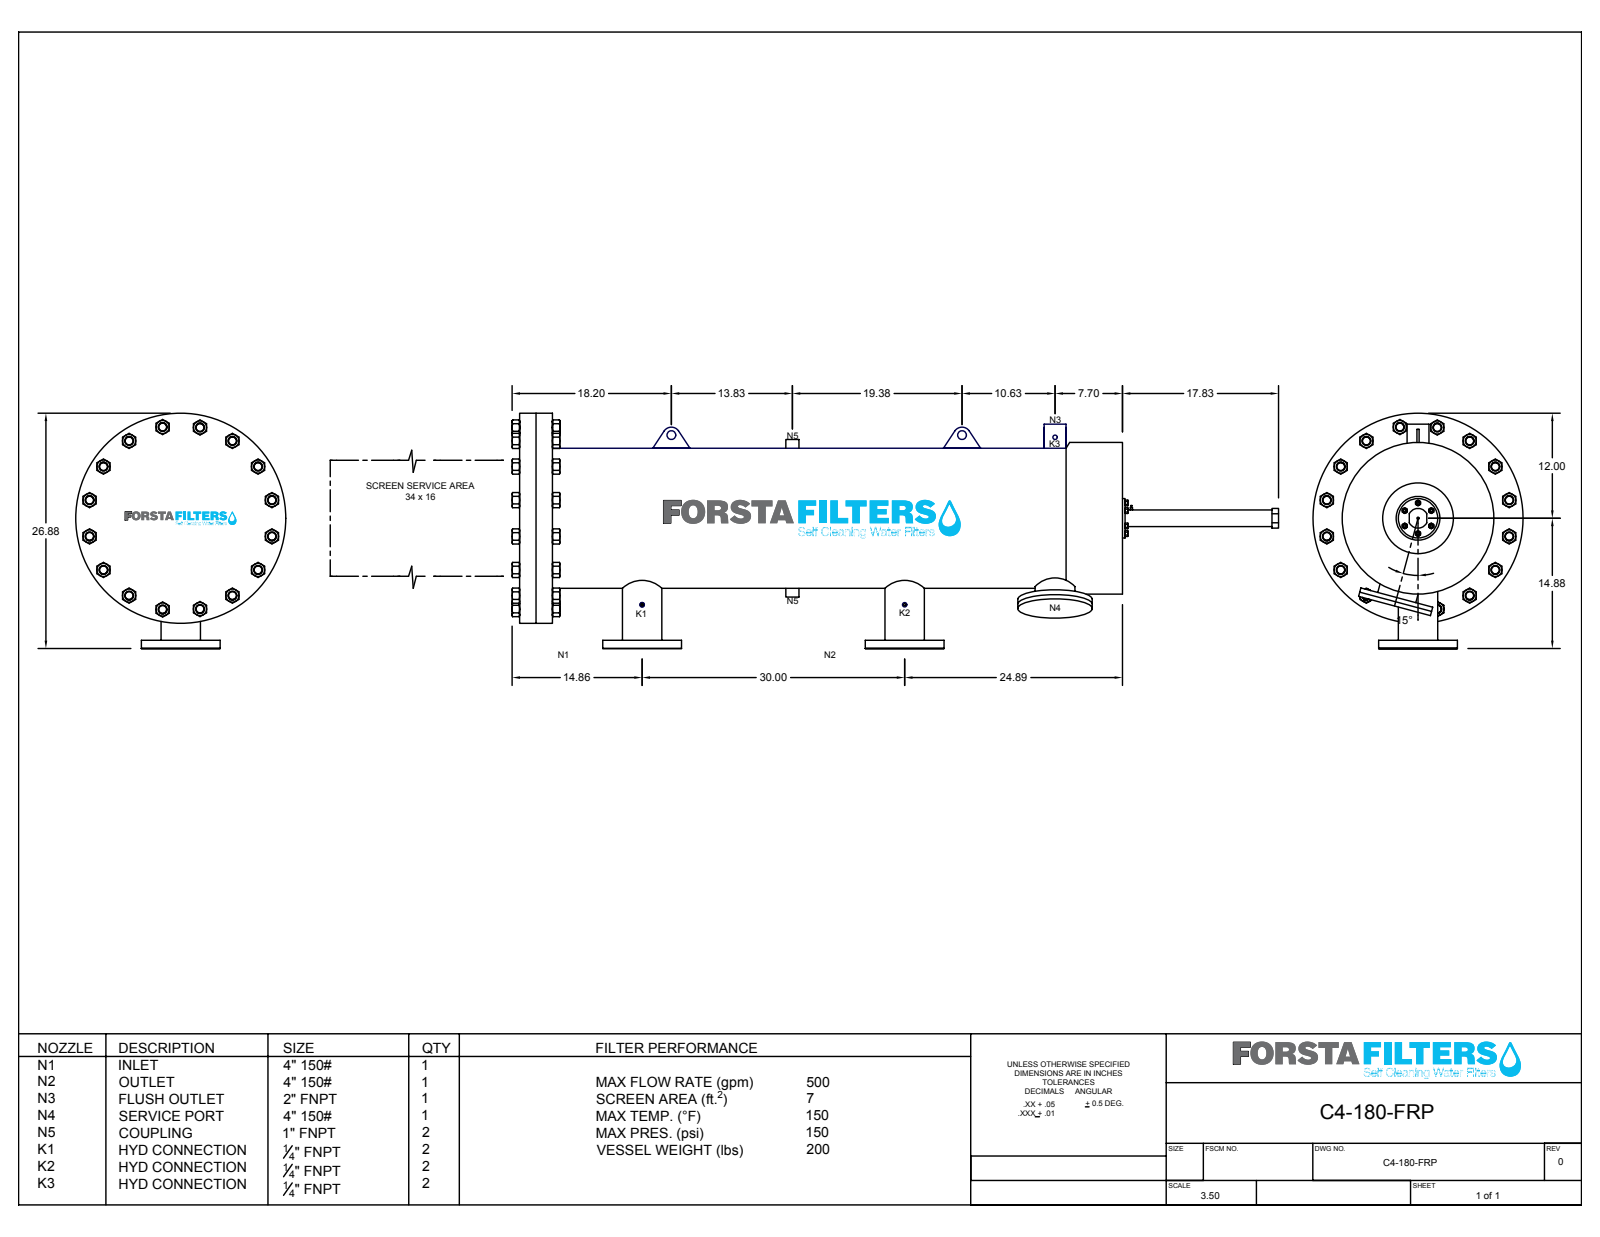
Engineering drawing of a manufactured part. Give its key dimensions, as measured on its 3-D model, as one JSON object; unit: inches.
{"part_name": "C4-FRP-180", "step_written_by": "SolidWorks 2018 (CONFIG_CONTROL_DESIGN)", "units": "inches", "bodies": {"solids": 22, "faces": 696, "planar": 362, "cylindrical": 330, "other": 4}, "overall_size": [87.395, 26.874, 24], "volume_in3": 2336, "surface_area_in2": 10796, "round_holes": [[0.75, 32], [1, 19], [4, 4], [0.25, 3], [0.246, 1], [1.507, 1], [2, 1], [15.603, 1], [16.934, 1]], "round_bosses_or_shafts": [[0.375, 6], [9, 4], [4.394, 4], [0.644, 2], [24, 1], [17.328, 1], [15.997, 1], [4.501, 1]], "partial_cylinders_radius": [[1, 2], [1.125, 1]], "face_to_face_distances": [1.875, 3.75, 1.875, 68.891, 67.016, 65.141, 68.694, 66.819, 64.944, 0.197], "hole_center_spacings": [2.87, 3.75, 5.303, 6.929, 4.146, 7.5, 8.132, 19.632]}
